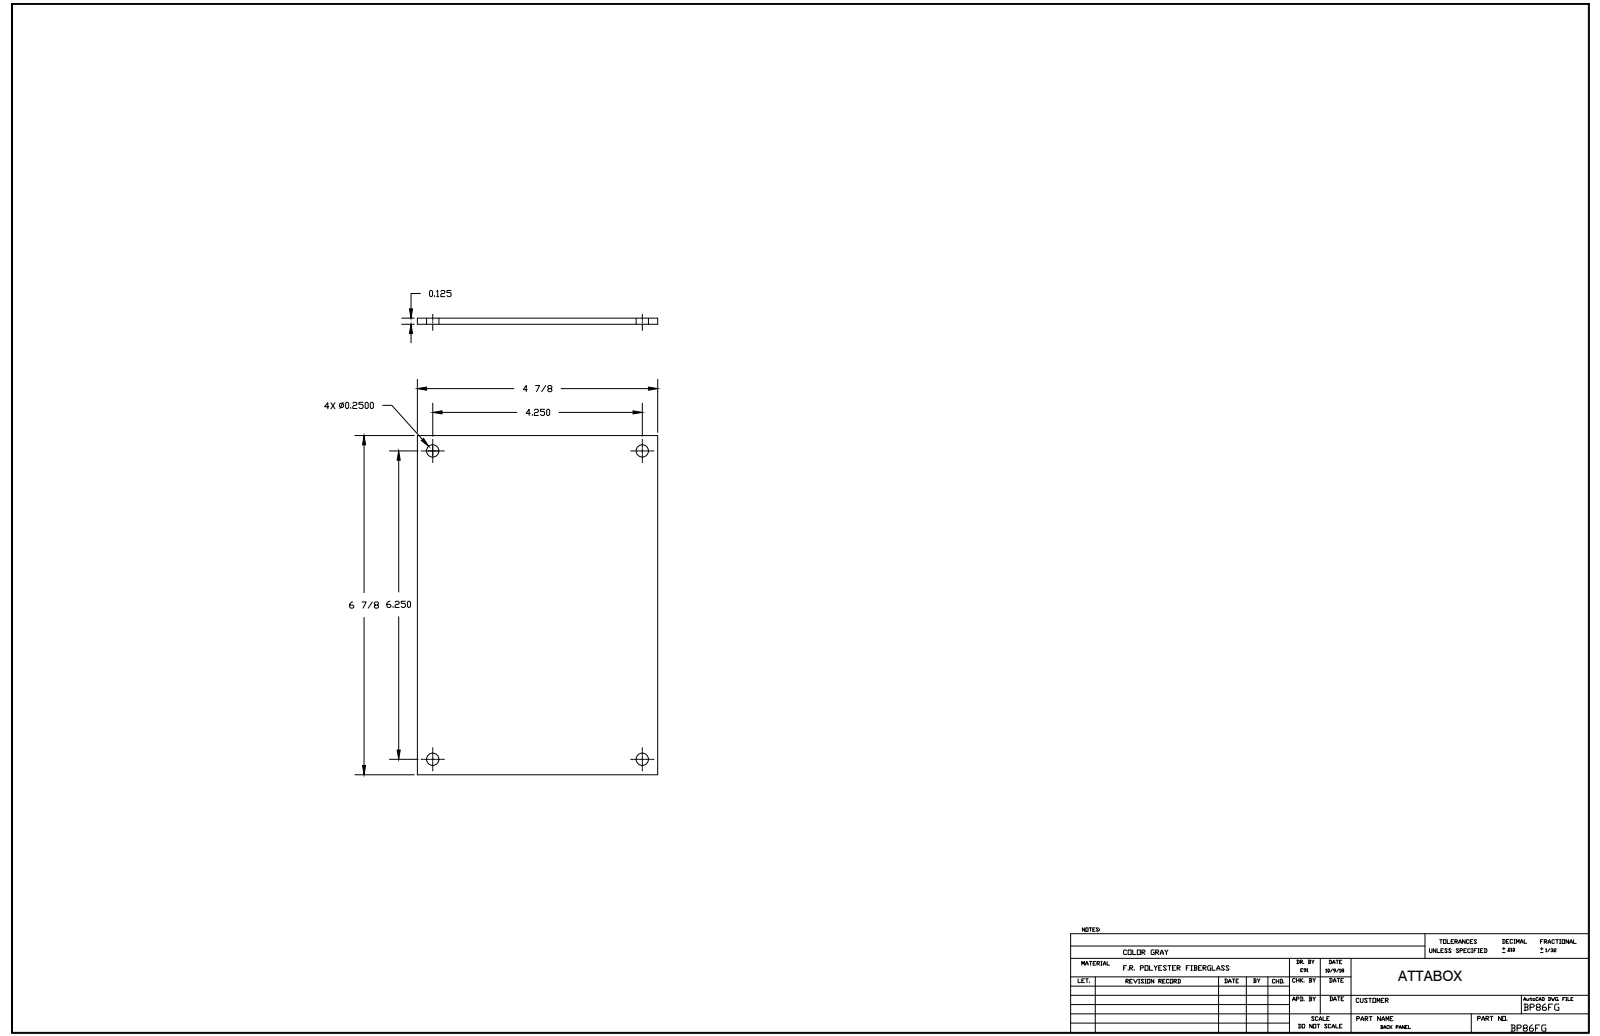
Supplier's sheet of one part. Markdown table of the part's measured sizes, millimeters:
| quantity | value |
| --- | --- |
| part name | BP86FG_STP |
| STEP written by | Autodesk Inventor 2014 (AUTOMOTIVE_DESIGN) |
| units | millimeters |
| bodies | 1 solid, 10 faces (6 planar, 4 cylindrical, 0 other) |
| overall size | 174.62 × 123.83 × 3.17 |
| volume | 68 251 mm³ |
| surface area | 45 141 mm² |
| round holes (diameter × count) | 6.35 × 4 |
| main face-to-face distances | 3.17, 123.82, 174.62 |
| hole center spacings | 107.94, 158.76, 191.98 |
